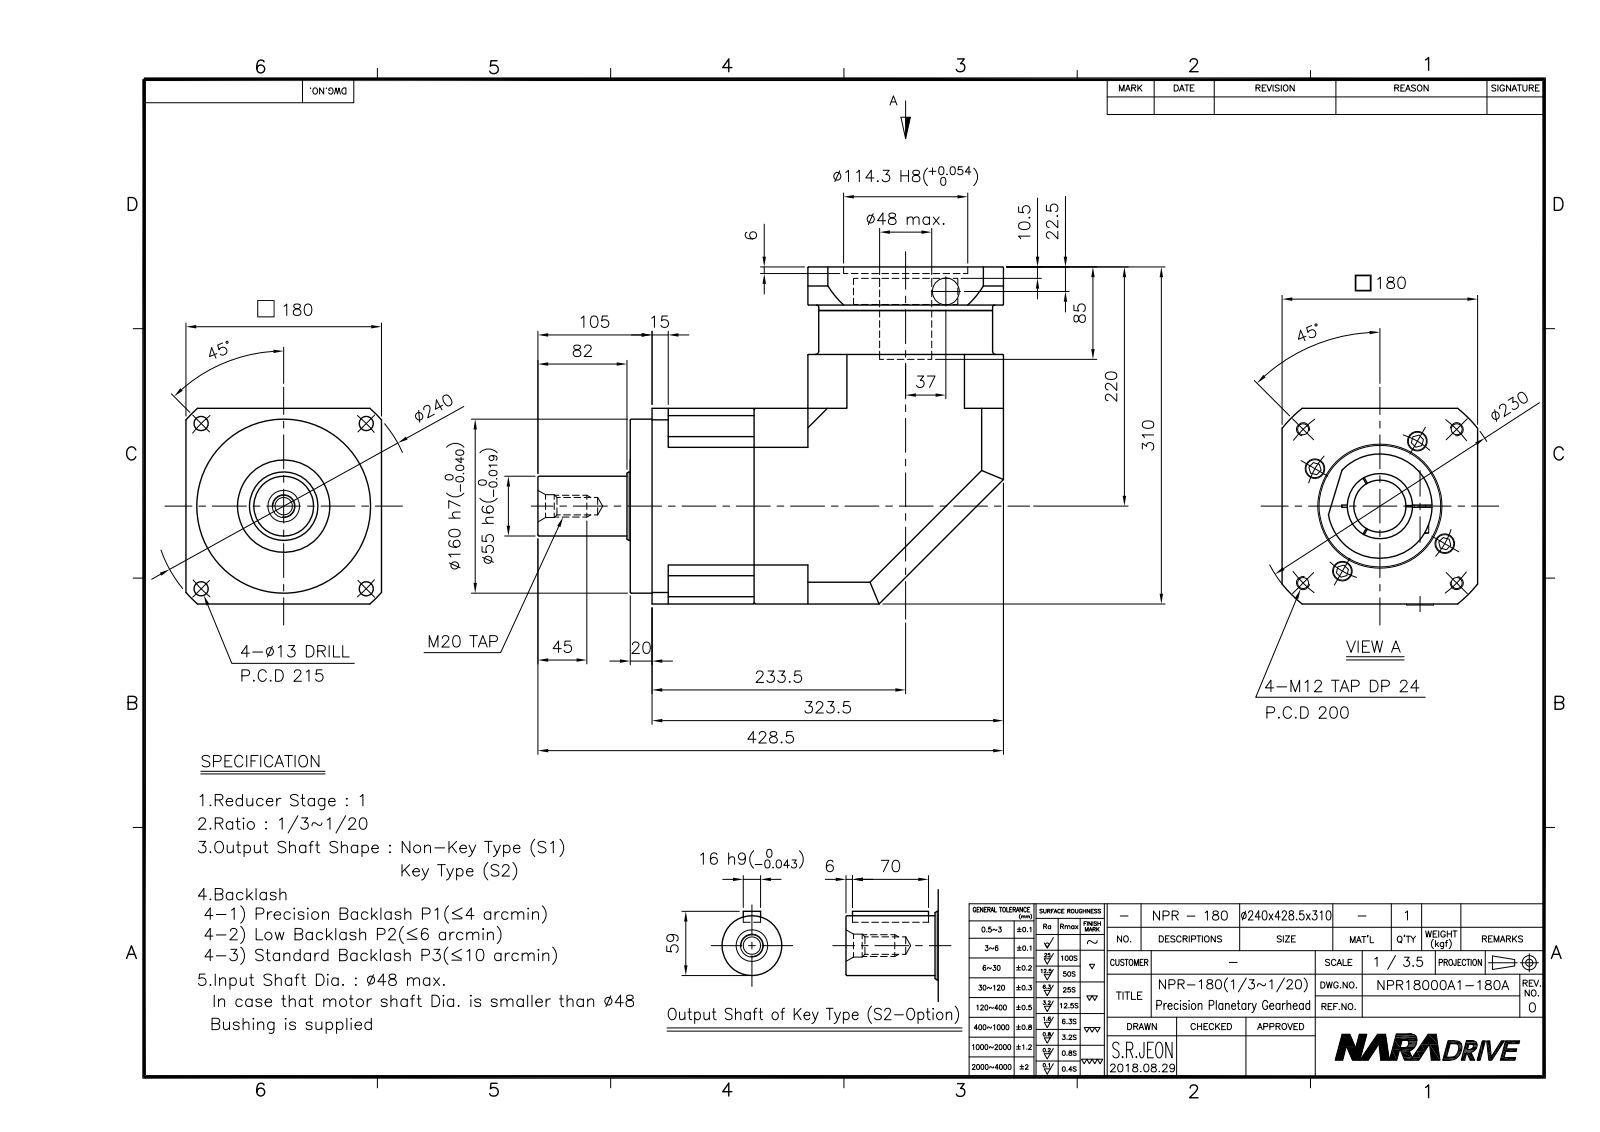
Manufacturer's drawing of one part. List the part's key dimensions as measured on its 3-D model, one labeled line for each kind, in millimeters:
Part name (STEP PRODUCT): NPR18000A1-180A-S1
STEP written by: Autodesk Inventor 2015 (AUTOMOTIVE_DESIGN)
Units: millimetres
Bodies: 2 solids, 523 faces (248 planar, 138 cylindrical, 137 other)
Overall size (bounding box): 428.5 × 310 × 181
Volume: 10 510 000 mm³ · Surface area: 608 649 mm²
Round holes (diameter × count): ⌀8.38 ×9, ⌀11 ×9, ⌀10.11 ×8, ⌀17.5 ×8, ⌀13 ×4, ⌀14 ×4, ⌀20 ×4, ⌀12.5 ×1, ⌀14.5 ×1, ⌀17.29 ×1, ⌀21 ×1, ⌀48 ×1
Round bosses / shafts (diameter × count): ⌀16 ×9, ⌀10 ×9, ⌀18 ×4, ⌀12 ×4, ⌀160 ×1, ⌀96 ×1, ⌀63 ×1, ⌀55 ×1
Partial cylindrical surfaces — rounded edges, fillets, slot ends (radius × count): R1 ×4, R2 ×4, R15 ×4, R105 ×2, R9 ×1, R115 ×1, R120 ×1
Main face-to-face distances: 180, 33, 310, 242.5, 209.5, 101, 130, 134, 20, 343.5
Hole centre spacings: 92.5, 158.93, 198.3, 122.33, 8, 30.04, 69, 135.4
